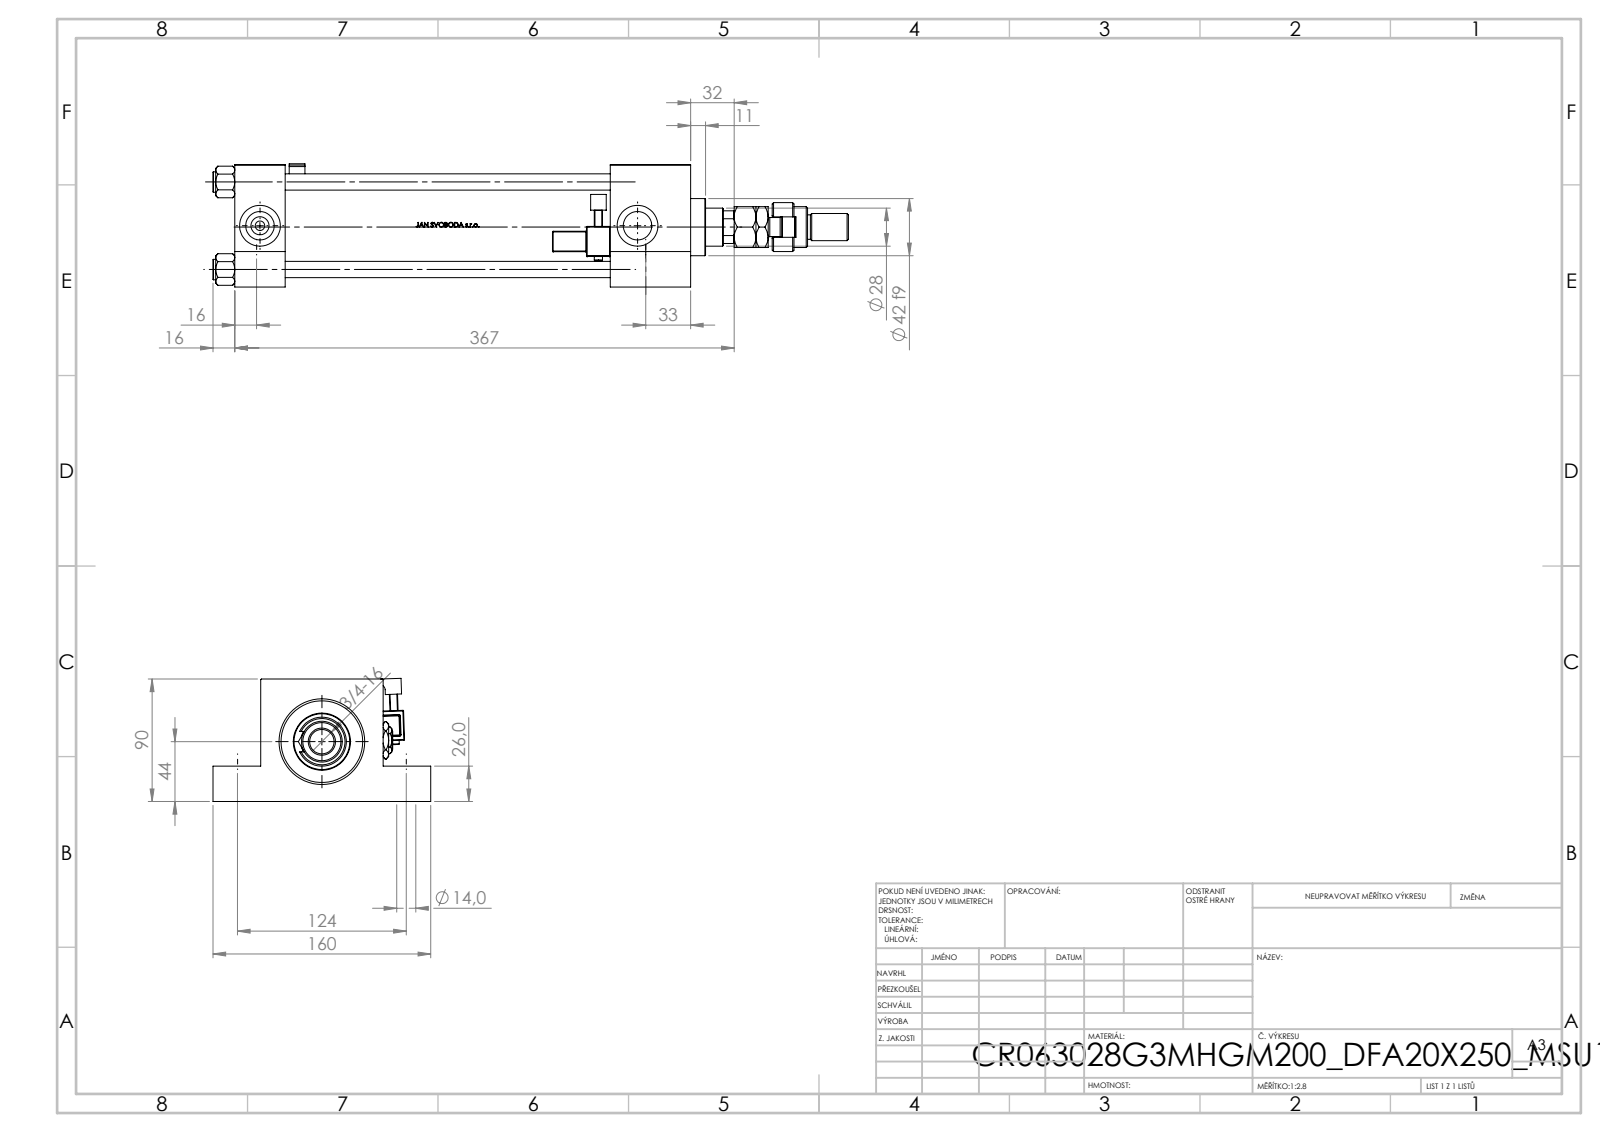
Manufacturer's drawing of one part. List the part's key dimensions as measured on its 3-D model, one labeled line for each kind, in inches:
Part name (STEP PRODUCT): FEMALE_PART_FOR_DFA; Zatka_pro_OIL_PORT; V215CR_G_TYCINKA; V215_VC_A (+5 more)
STEP written by: SolidWorks 2019 (CONFIG_CONTROL_DESIGN)
Units: inches
Bodies: 17 solids, 1423 faces (564 planar, 205 cylindrical, 654 other)
Overall size (bounding box): 18.386 × 6.299 × 3.564
Volume: 91.78 in³ · Surface area: 538.6 in²
Round holes (diameter × count): ⌀0.472 ×4, ⌀0.551 ×4, ⌀0.276 ×2, ⌀0.825 ×2, ⌀1.181 ×2, ⌀0.728 ×1, ⌀1.102 ×1, ⌀1.22 ×1, ⌀1.969 ×1, ⌀2.362 ×1, ⌀2.48 ×1
Round bosses / shafts (diameter × count): ⌀0.591 ×4, ⌀0.236 ×2, ⌀2.717 ×1, ⌀1.654 ×1, ⌀1.417 ×1, ⌀1.181 ×1, ⌀0.866 ×1, ⌀0.787 ×1
Partial cylindrical surfaces — rounded edges, fillets, slot ends (radius × count): R0.02 ×48, R0.039 ×2, R0.098 ×2, R0.157 ×2, R0.236 ×1, R0.295 ×1, R0.472 ×1, R0.531 ×1
Main face-to-face distances: 3.543, 1.457, 13.189, 11.732, 2.323, 10.866, 9.409, 1.024, 2.52, 1.378
Hole centre spacings: 2.531, 1.763, 1.818, 3.58, 4.882, 11.26, 12.272, 10.925
